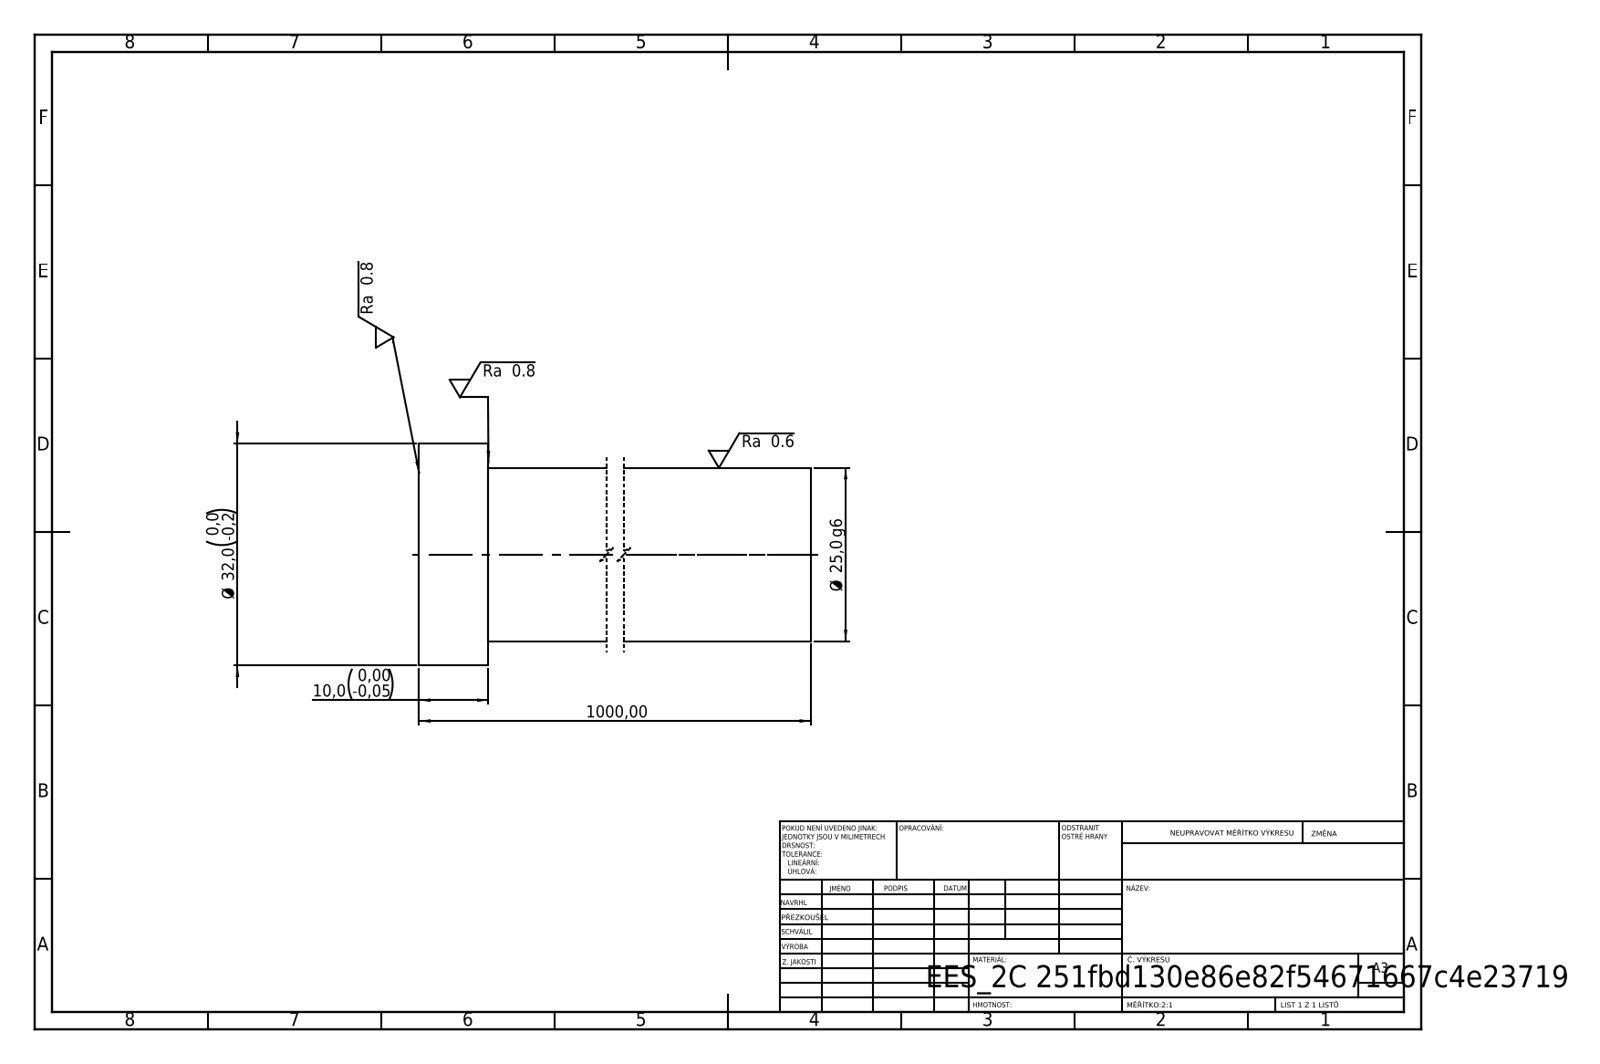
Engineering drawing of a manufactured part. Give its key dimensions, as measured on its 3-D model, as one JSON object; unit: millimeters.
{"step_written_by": "SolidWorks 2019 (CONFIG_CONTROL_DESIGN)", "units": "millimeters", "bodies": {"solids": 1, "faces": 7, "planar": 3, "cylindrical": 4, "other": 0}, "overall_size": [1000, 32, 32], "volume_mm3": 494008, "surface_area_mm2": 80368, "round_bosses_or_shafts": [[32, 1], [25, 1]], "face_to_face_distances": [1000, 10, 990]}
